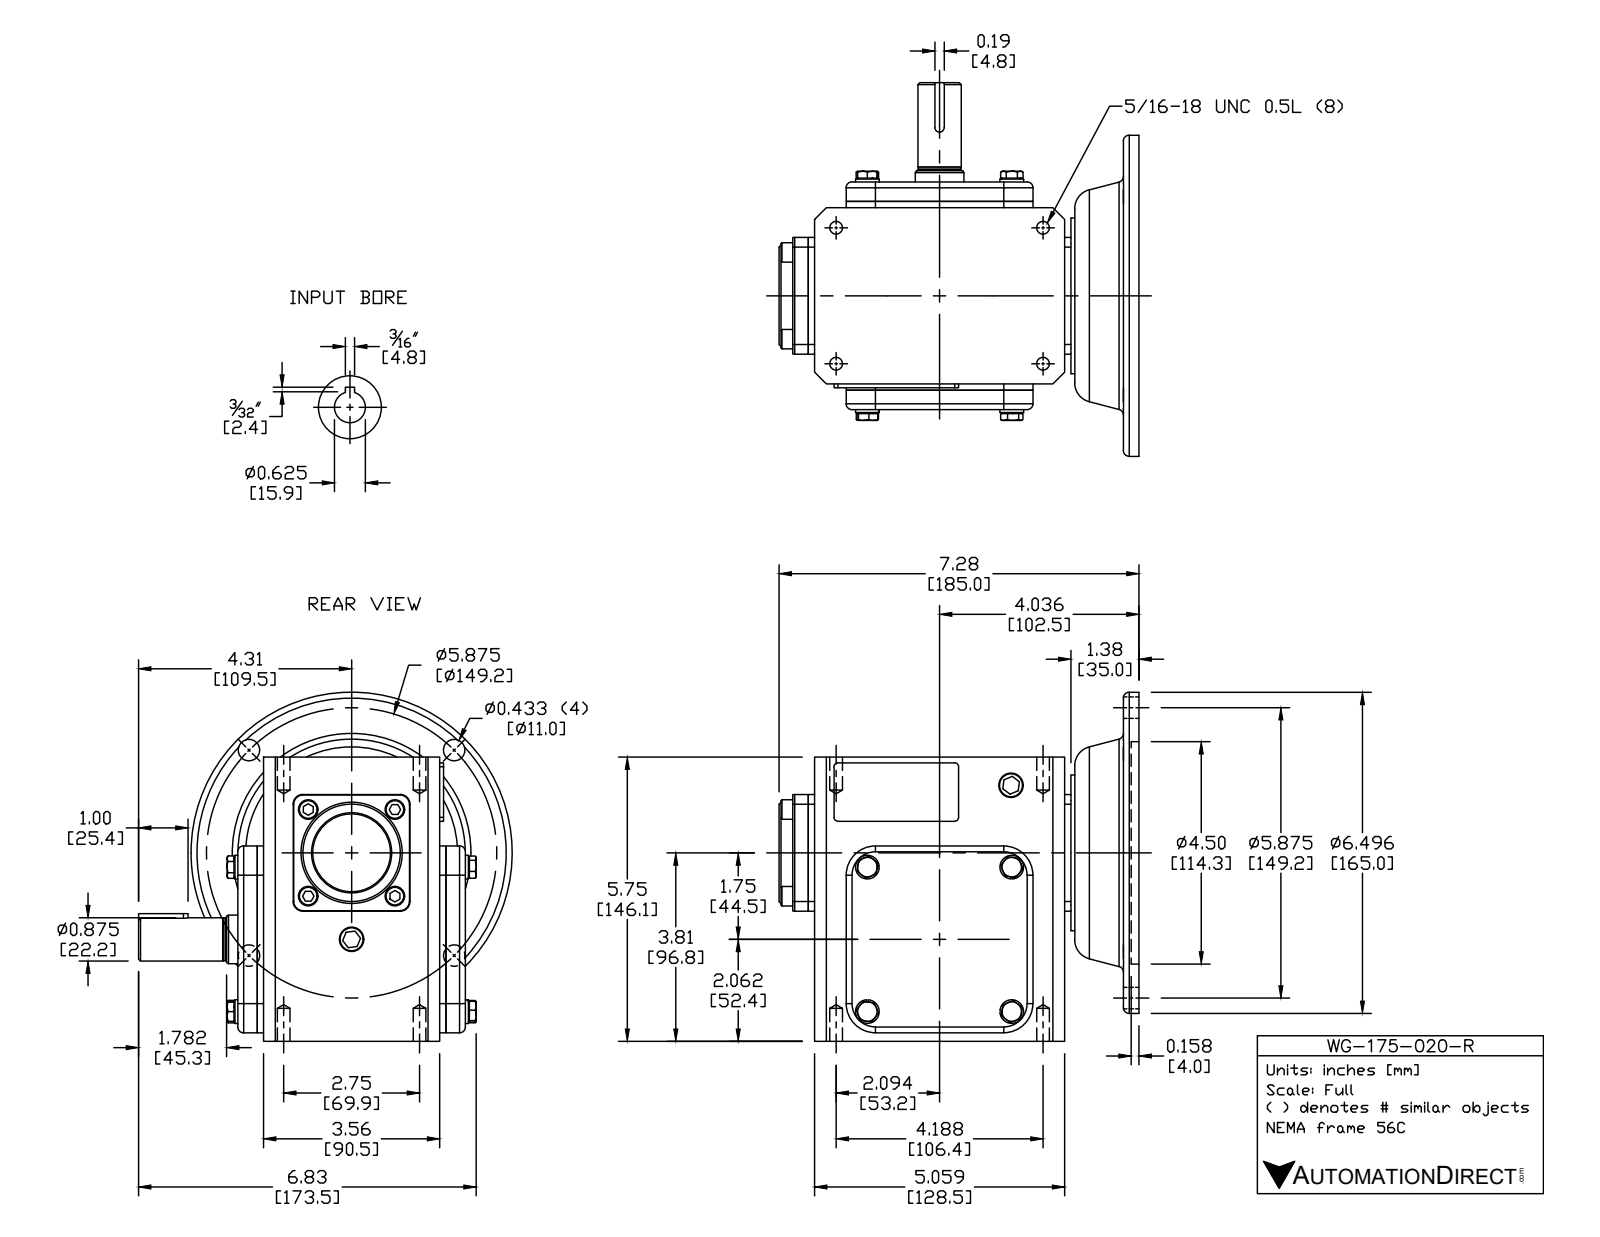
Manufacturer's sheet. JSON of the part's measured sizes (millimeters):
{"part_name": "WG-175-020-R", "step_written_by": "SolidWorks 2015 (CONFIG_CONTROL_DESIGN)", "units": "millimeters", "bodies": {"solids": 43, "faces": 613, "planar": 312, "cylindrical": 172, "other": 129}, "overall_size": [192, 185, 179.3], "volume_mm3": 2161000, "surface_area_mm2": 236400, "round_holes": [[6.5, 4], [10.3, 4], [13, 1], [15.9, 1], [25, 1], [30, 1], [37, 1], [40, 1], [90, 1], [114.3, 1]], "round_bosses_or_shafts": [[10, 8], [12.2, 4], [13, 2], [165, 1], [80, 1], [52, 1], [40, 1], [22.2, 1]], "partial_cylinders_radius": [[2, 8], [3, 8], [5, 4], [15, 4], [0.5, 2], [1, 2], [2.4, 1]], "face_to_face_distances": [3.3, 97, 107, 10, 103.8, 93.8, 13.3, 8, 146.1, 170], "hole_center_spacings": [74.6, 105.5, 53.4, 69.9, 106.4, 110.6, 127.3, 149.2]}
